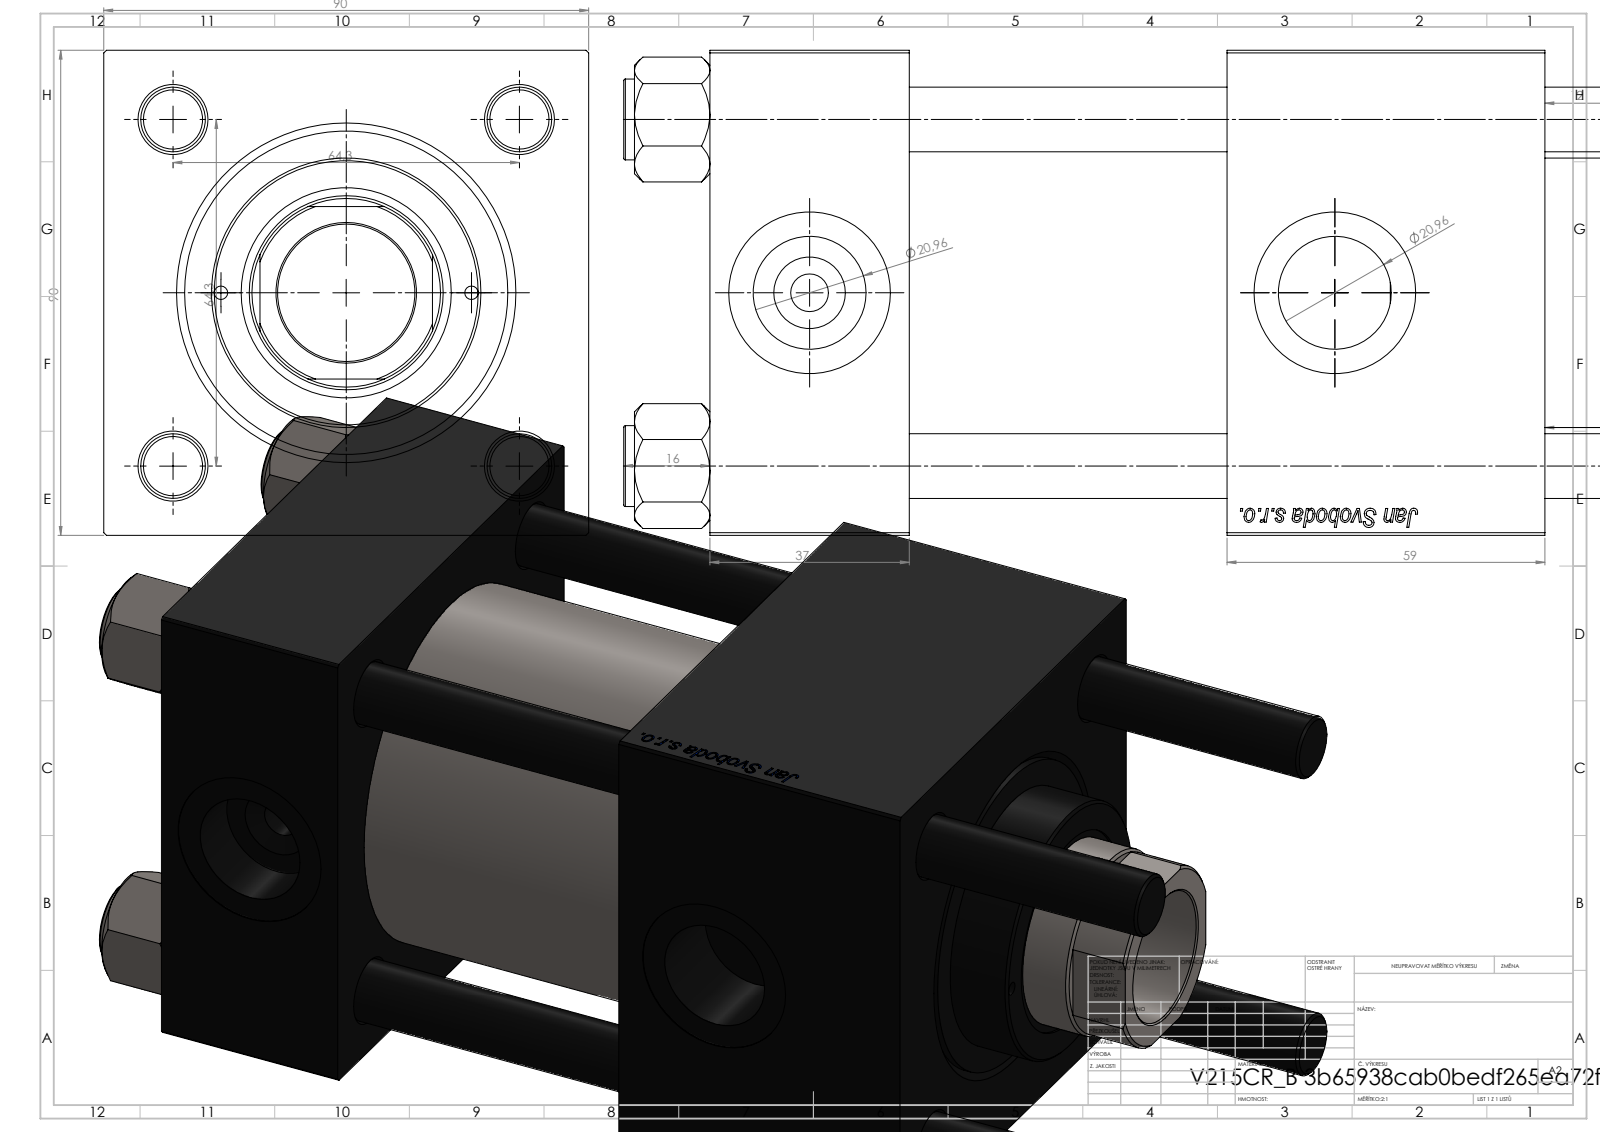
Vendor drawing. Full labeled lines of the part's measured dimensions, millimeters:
Part name (STEP PRODUCT): V215CR_VCP_B; V215CR_B-1; V215_VC_A; V215CR_B_TYCINKA (+1 more)
STEP written by: SolidWorks 2019 (CONFIG_CONTROL_DESIGN)
Units: millimetres
Bodies: 11 solids, 1164 faces (434 planar, 82 cylindrical, 648 other)
Overall size (bounding box): 217 × 90 × 90
Volume: 1 002 000 mm³ · Surface area: 200 383 mm²
Round holes (diameter × count): ⌀12 ×4, ⌀2.5 ×2, ⌀7 ×2, ⌀20.96 ×2, ⌀30 ×2, ⌀25.5 ×1, ⌀36 ×1, ⌀39 ×1, ⌀50 ×1, ⌀60 ×1, ⌀63 ×1
Round bosses / shafts (diameter × count): ⌀15 ×4, ⌀69 ×1
Partial cylindrical surfaces — rounded edges, fillets, slot ends (radius × count): R17.5 ×1
Main face-to-face distances: 90, 59, 37, 155, 118, 96, 126.3, 89.3, 30.3, 28.7
Hole centre spacings: 33.36, 45.47, 64.05, 64.3, 23.25, 90.93, 46.5, 97.5
